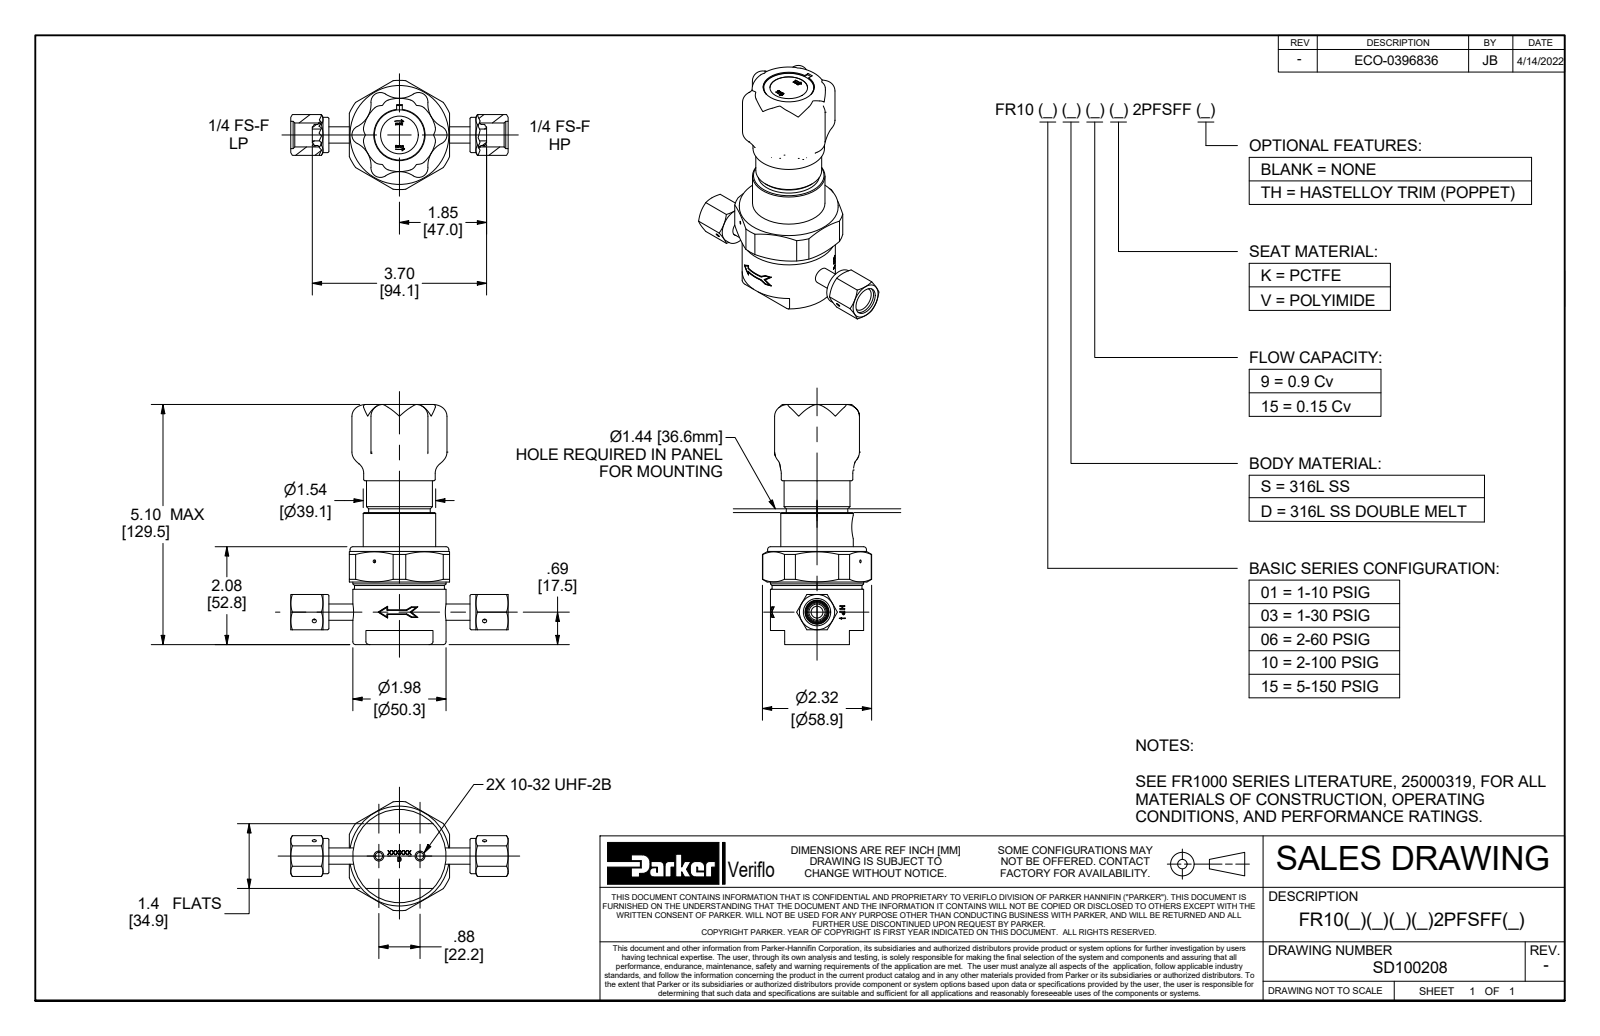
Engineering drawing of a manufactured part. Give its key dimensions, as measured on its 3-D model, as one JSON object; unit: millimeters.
{"part_name": "SD100208", "step_written_by": "Autodesk Inventor 2020 (AUTOMOTIVE_DESIGN)", "units": "millimeters", "bodies": {"solids": 1, "faces": 518, "planar": 278, "cylindrical": 103, "other": 137}, "overall_size": [129.5, 117.3, 58.9], "volume_mm3": 218100, "surface_area_mm2": 32160, "round_holes": [[2.3, 2], [4, 2], [1.6, 1], [6.4, 1], [9.2, 1], [12.9, 1], [14.7, 1], [20.3, 1], [27.7, 1]], "round_bosses_or_shafts": [[53.3, 1], [50.3, 1], [48.5, 1], [39.1, 1], [38.6, 1], [35.6, 1], [33.2, 1], [27.1, 1]], "partial_cylinders_radius": [[5.1, 6], [6, 6], [13.5, 6], [0.3, 4], [0.4, 4], [0.3, 2], [0.4, 2], [0.6, 2]], "face_to_face_distances": [19.1, 54.1, 52.8, 25.8, 129.1, 76.3, 0.5, 129.5, 76.7, 7.6], "hole_center_spacings": [11.1, 22.2, 91.9]}
